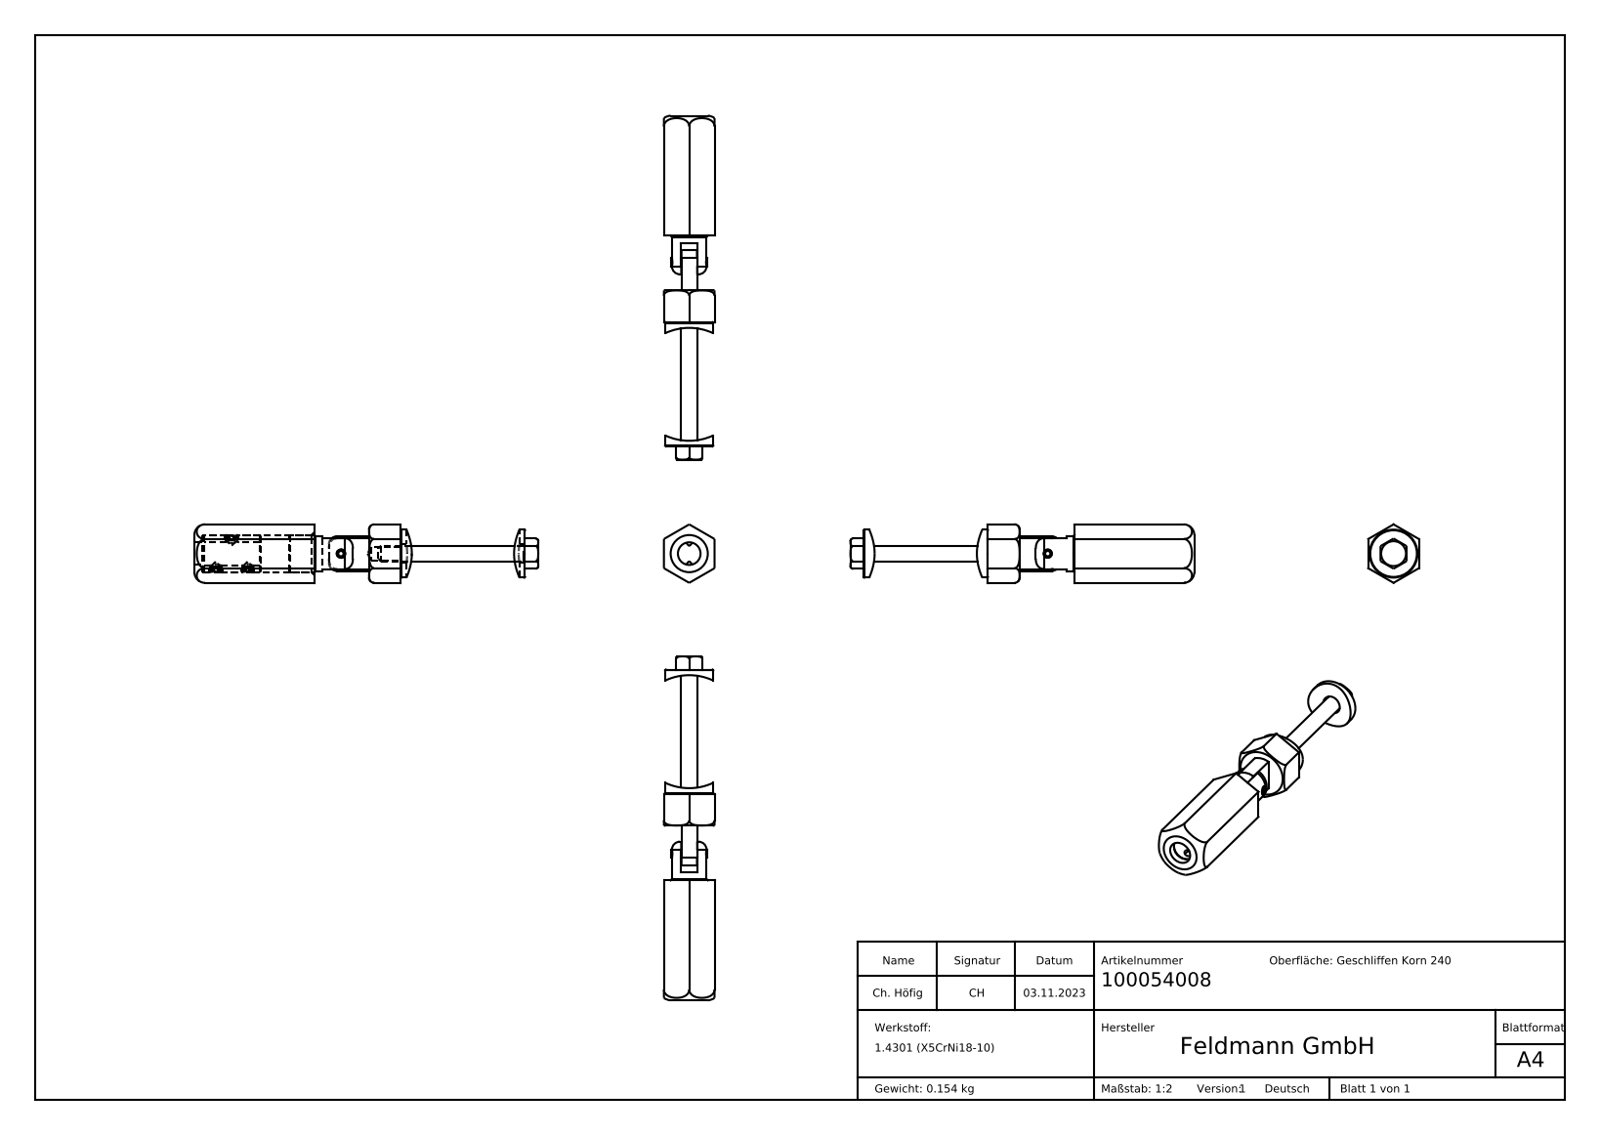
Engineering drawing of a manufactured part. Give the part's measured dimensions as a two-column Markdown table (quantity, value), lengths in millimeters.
| quantity | value |
| --- | --- |
| part name | 10005400X Teil7_100054x04 Teil7; 10005400X Teil5_100054x08 Teil5; 10005400X Teil2_100054x08 Teil2; 10005400X Teil6_100054008 Teil6 (+5 more) |
| STEP written by | SolidWorks 2018 (CONFIG_CONTROL_DESIGN) |
| units | millimeters |
| bodies | 11 solids, 345 faces (174 planar, 28 cylindrical, 143 other) |
| overall size | 129.12 × 21.94 × 19 |
| volume | 19 451 mm³ |
| surface area | 13 652 mm² |
| round holes (diameter × count) | 4.2 × 3, 2 × 1, 3.1 × 1, 3.2 × 1, 5 × 1, 7 × 1, 8.5 × 1, 9 × 1 |
| round bosses / shafts (diameter × count) | 5 × 3, 18 × 1, 14 × 1, 13 × 1, 6 × 1, 3 × 1 |
| partial cylindrical surfaces (radius × count) | 21.2 × 1 |
| main face-to-face distances | 19, 6.6, 12.4, 46.6, 6.5, 12.5, 5.9, 12, 58.6, 4.6 |
| hole center spacings | 6, 12 |
